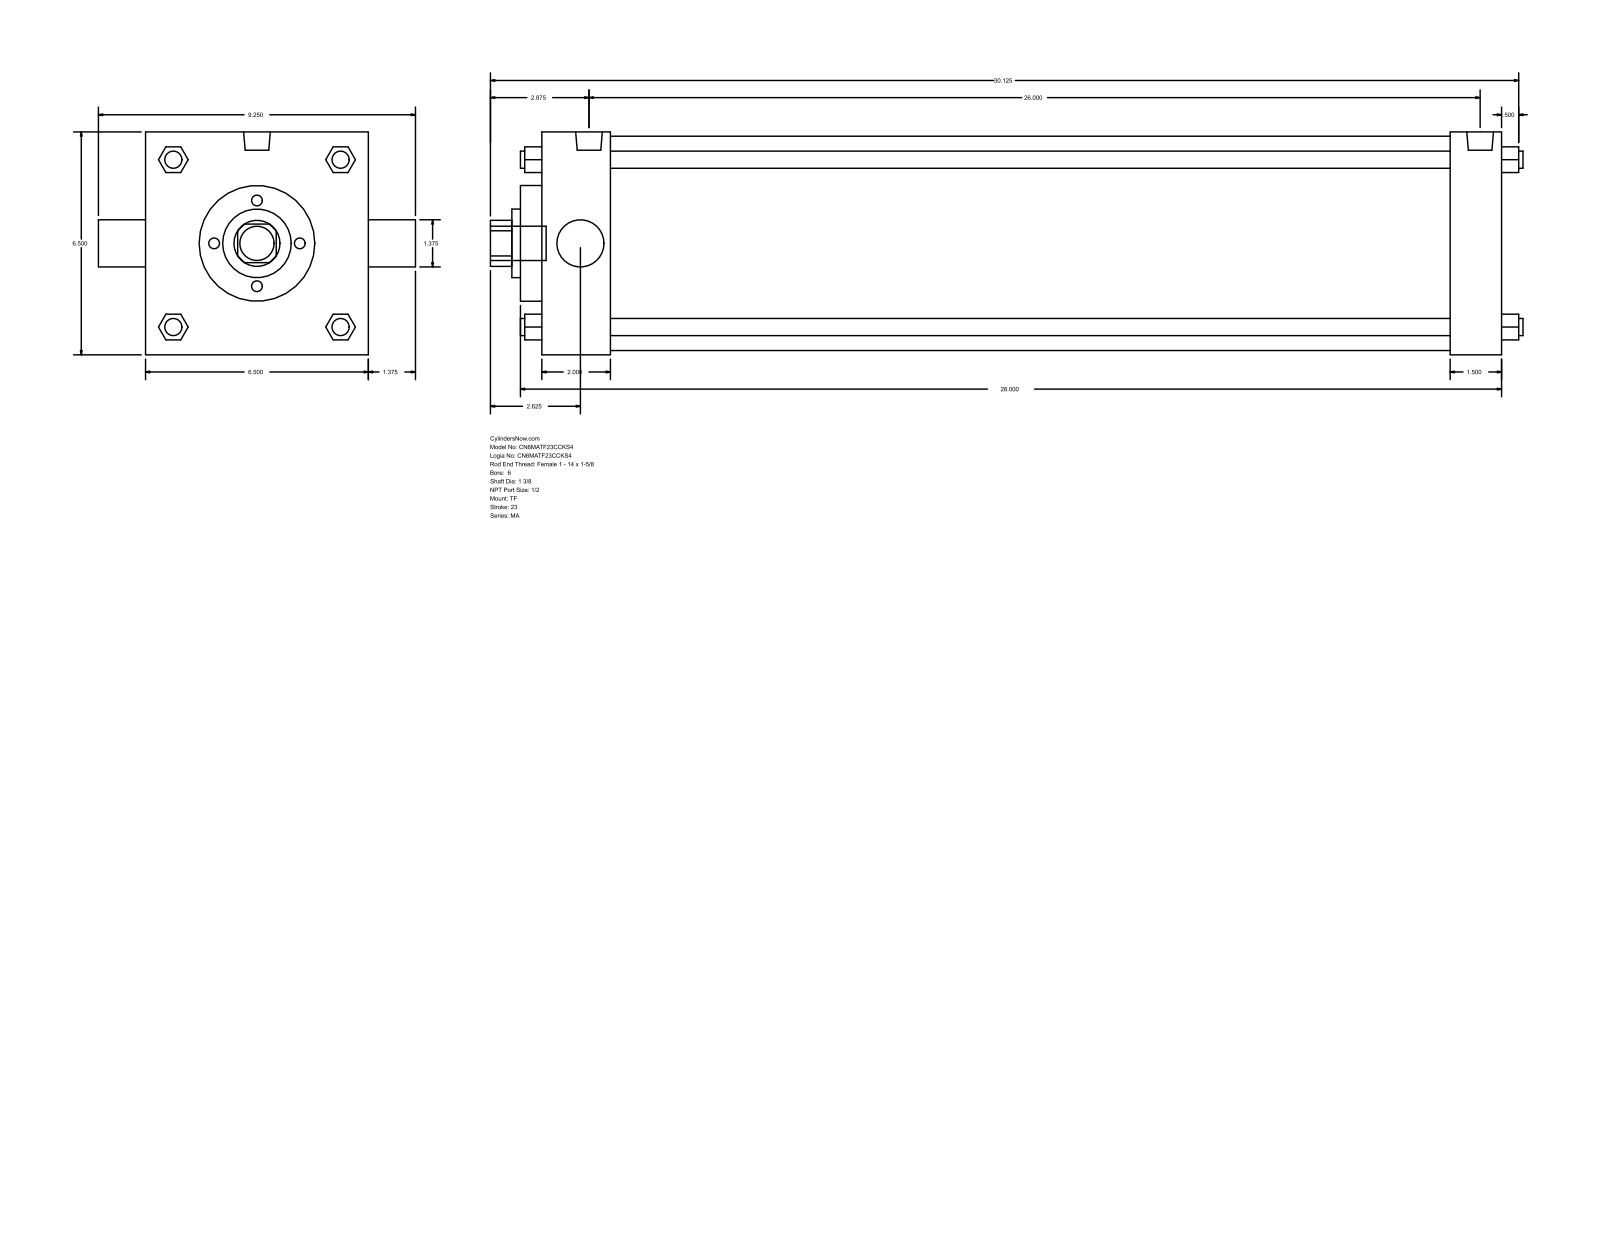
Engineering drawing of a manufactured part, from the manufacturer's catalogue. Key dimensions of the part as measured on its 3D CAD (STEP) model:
Part name (STEP PRODUCT): MA_TF__0600_1.375
STEP written by: GSSL Pune (CONFIG_CONTROL_DESIGN)
Units: millimetres
Bodies: 0 solids, 122 faces (93 planar, 29 cylindrical, 0 other)
Overall size (bounding box): 765.17 × 234.95 × 165.1
Round holes (diameter × count): ⌀34.92 ×2, ⌀50.8 ×1, ⌀85.72 ×1, ⌀158.75 ×1
Round bosses / shafts (diameter × count): ⌀12.7 ×4, ⌀17.46 ×3, ⌀19.77 ×2, ⌀25.4 ×1
Partial cylindrical surfaces — rounded edges, fillets, slot ends (radius × count): R17.06 ×1
Main face-to-face distances: 165.1, 714.38, 38.1, 50.8, 663.58, 676.28, 625.48, 15.87, 66.67, 692.15
